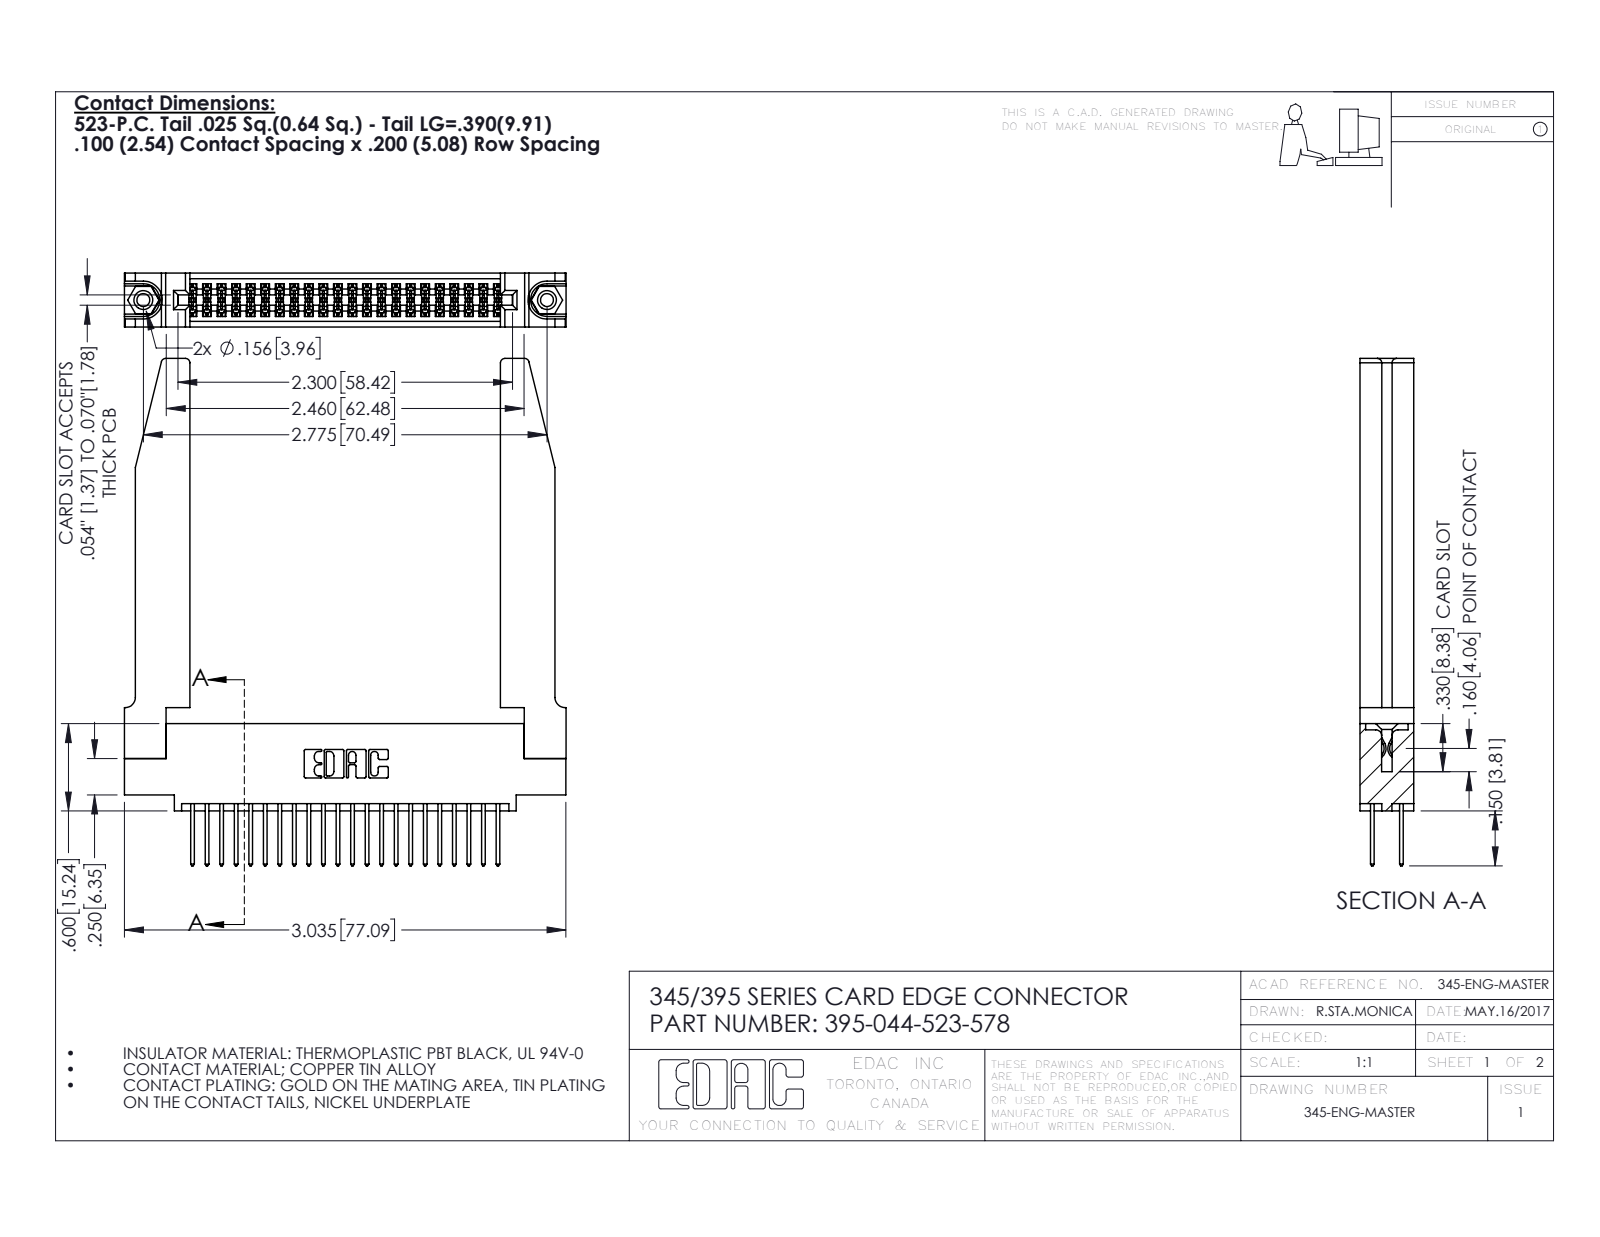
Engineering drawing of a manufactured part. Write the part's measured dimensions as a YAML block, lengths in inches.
part_name: "345-292-001_345-293-123; 345 Part_0.110 Offset - 0.156 Dia-TH; 345-220-078_345-220-078; 345-250-001_345-250-001-102 (+1 more)"
step_written_by: "SolidWorks 2016 (CONFIG_CONTROL_DESIGN)"
units: inches
bodies: {solids: 49, faces: 2564, planar: 1678, cylindrical: 834, other: 52}
overall_size: [3.487, 3.036, 0.37]
volume: 0.921
surface_area: 27.55
round_holes:
  - {diameter: 0.089, count: 2}
  - {diameter: 0.125, count: 2}
  - {diameter: 0.156, count: 2}
  - {diameter: 0.064, count: 1}
round_bosses_or_shafts:
  - {diameter: 0.155, count: 2}
partial_cylinders:
  - {radius: 0.006, count: 66}
  - {radius: 0.01, count: 44}
  - {radius: 0.01, count: 22}
  - {radius: 0.03, count: 8}
  - {radius: 0.007, count: 6}
  - {radius: 0.031, count: 6}
  - {radius: 0.026, count: 3}
  - {radius: 0.014, count: 2}
face_to_face_distances: [0.37, 0.072, 0.298, 0.2, 0.098, 0.272, 0.025, 0.225, 0.148, 0.15]
hole_center_spacings: [0.27, 2.541, 2.775]
